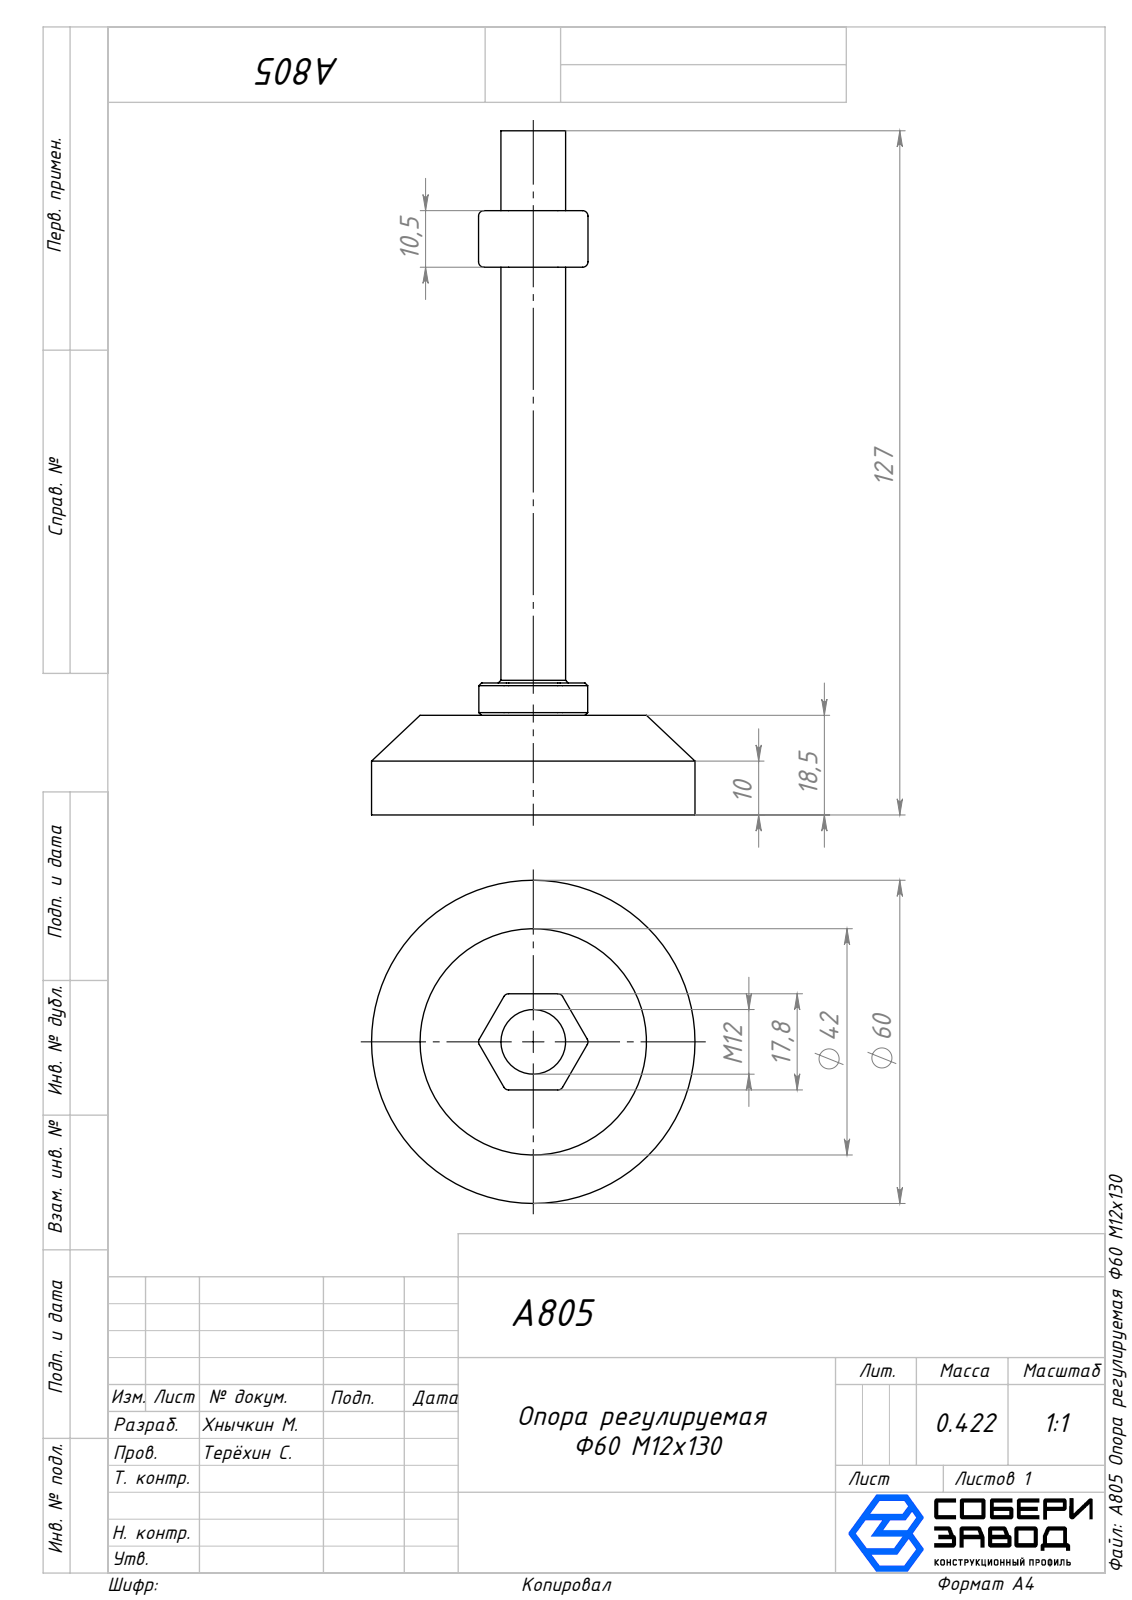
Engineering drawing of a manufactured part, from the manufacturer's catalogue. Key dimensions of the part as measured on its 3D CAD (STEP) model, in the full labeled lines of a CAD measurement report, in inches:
Part name (STEP PRODUCT): Вал M12_00; hex bolt gradeab_din_DIN EN 24014 - M5 x 25 x 16-N; Гайка М12_00; A805 Опора регулируемая Ф60 М12х130 (+1 more)
STEP written by: SolidWorks 2025 (AUTOMOTIVE_DESIGN)
Units: inches
Bodies: 4 solids, 140 faces (48 planar, 44 cylindrical, 48 other)
Overall size (bounding box): 5 × 2.362 × 2.362
Volume: 3.569 in³ · Surface area: 25.01 in²
Round holes (diameter × count): ⌀0.205 ×1, ⌀0.394 ×1, ⌀0.906 ×1
Round bosses / shafts (diameter × count): ⌀2.362 ×1, ⌀0.472 ×1, ⌀0.315 ×1, ⌀0.197 ×1
Partial cylindrical surfaces — rounded edges, fillets, slot ends (radius × count): R0.039 ×24
Main face-to-face distances: 0.728, 0.276, 0.453, 0.701, 0.702, 0.699, 0.02, 0.965, 0.256, 0.472
